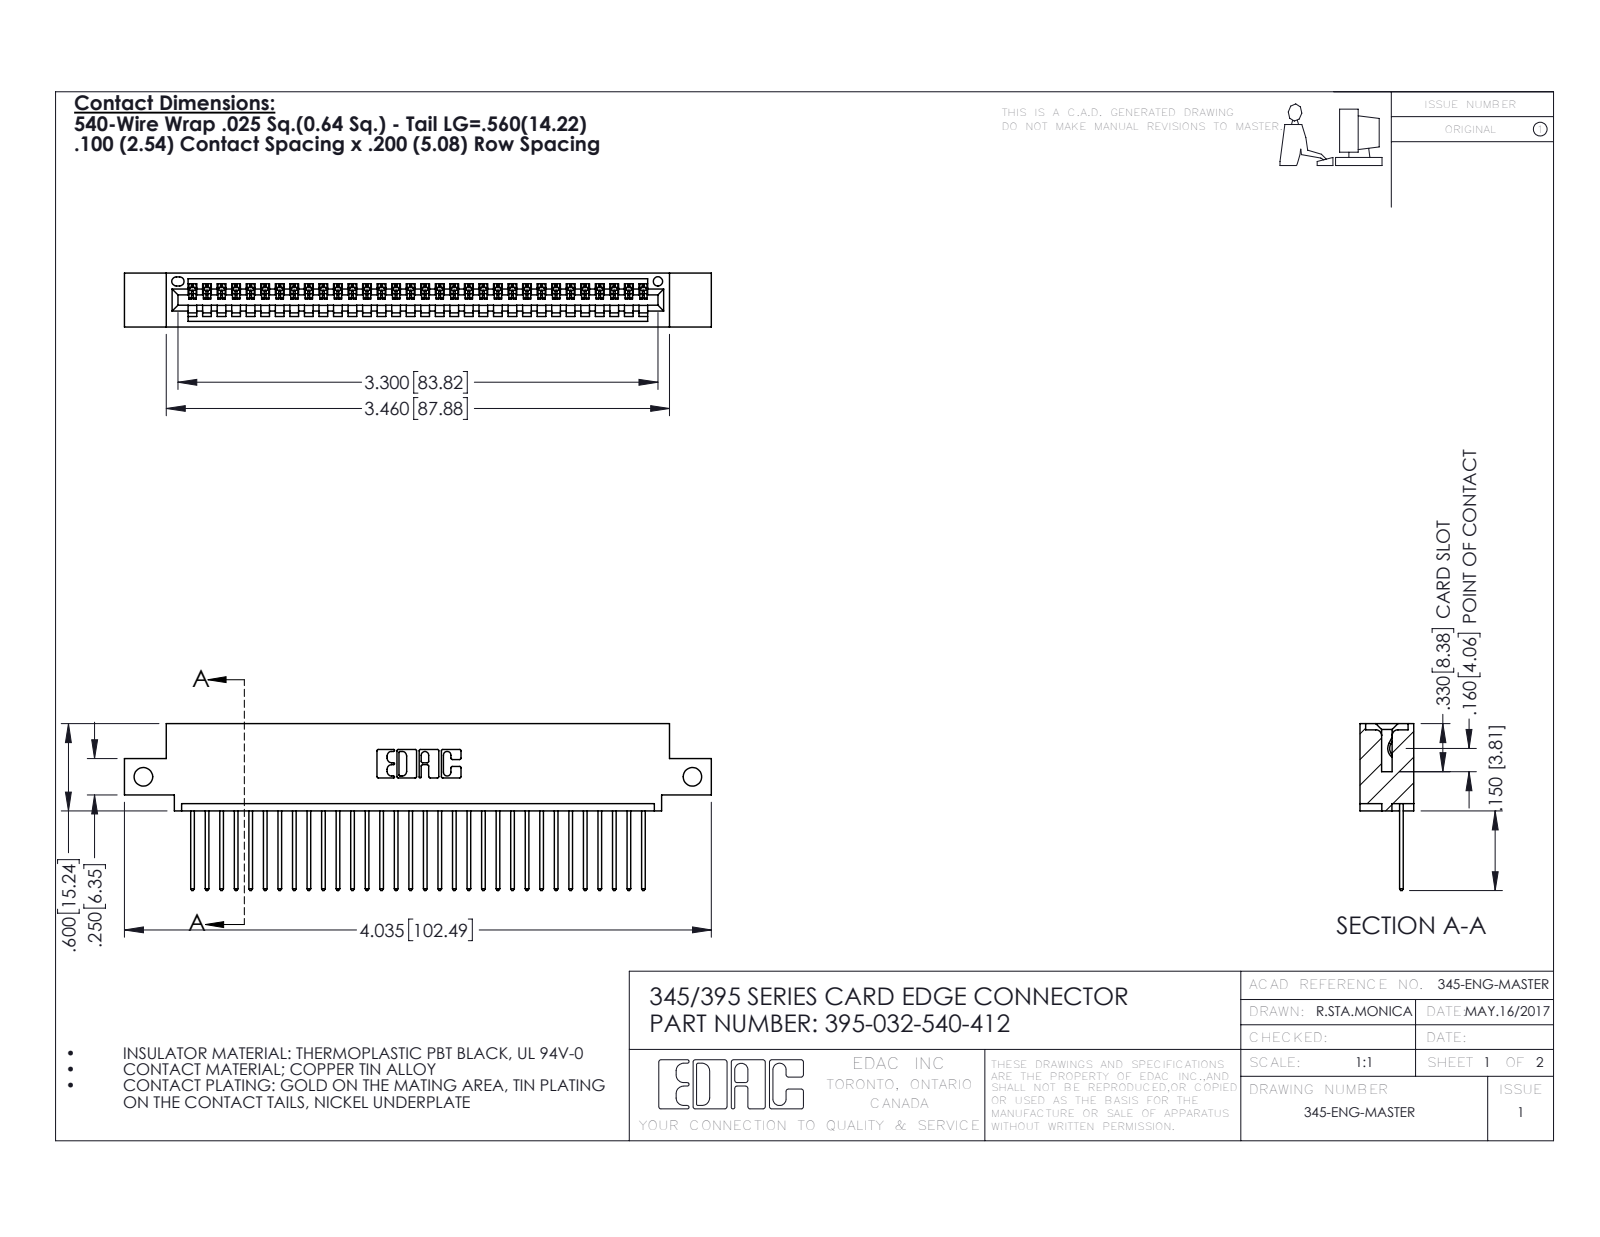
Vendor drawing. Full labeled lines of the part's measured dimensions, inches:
Part name (STEP PRODUCT): 345-292-001_345-293-140; 345 Part_0.110 Offset - Side Mount; 395-032-540-412
STEP written by: SolidWorks 2016 (CONFIG_CONTROL_DESIGN)
Units: inches
Bodies: 33 solids, 1986 faces (1364 planar, 622 cylindrical, 0 other)
Overall size (bounding box): 4.035 × 1.147 × 0.37
Volume: 0.582 in³ · Surface area: 19.82 in²
Round holes (diameter × count): ⌀0.128 ×2, ⌀0.064 ×1
Partial cylindrical surfaces — rounded edges, fillets, slot ends (radius × count): R0.006 ×64, R0.01 ×64, R0.01 ×22, R0.007 ×6, R0.031 ×6, R0.026 ×3, R0.031 ×2, R0.04 ×2
Main face-to-face distances: 0.298, 0.072, 0.37, 0.2, 0.098, 0.272, 0.025, 0.225, 0.149, 0.072
Hole centre spacings: 3.775
